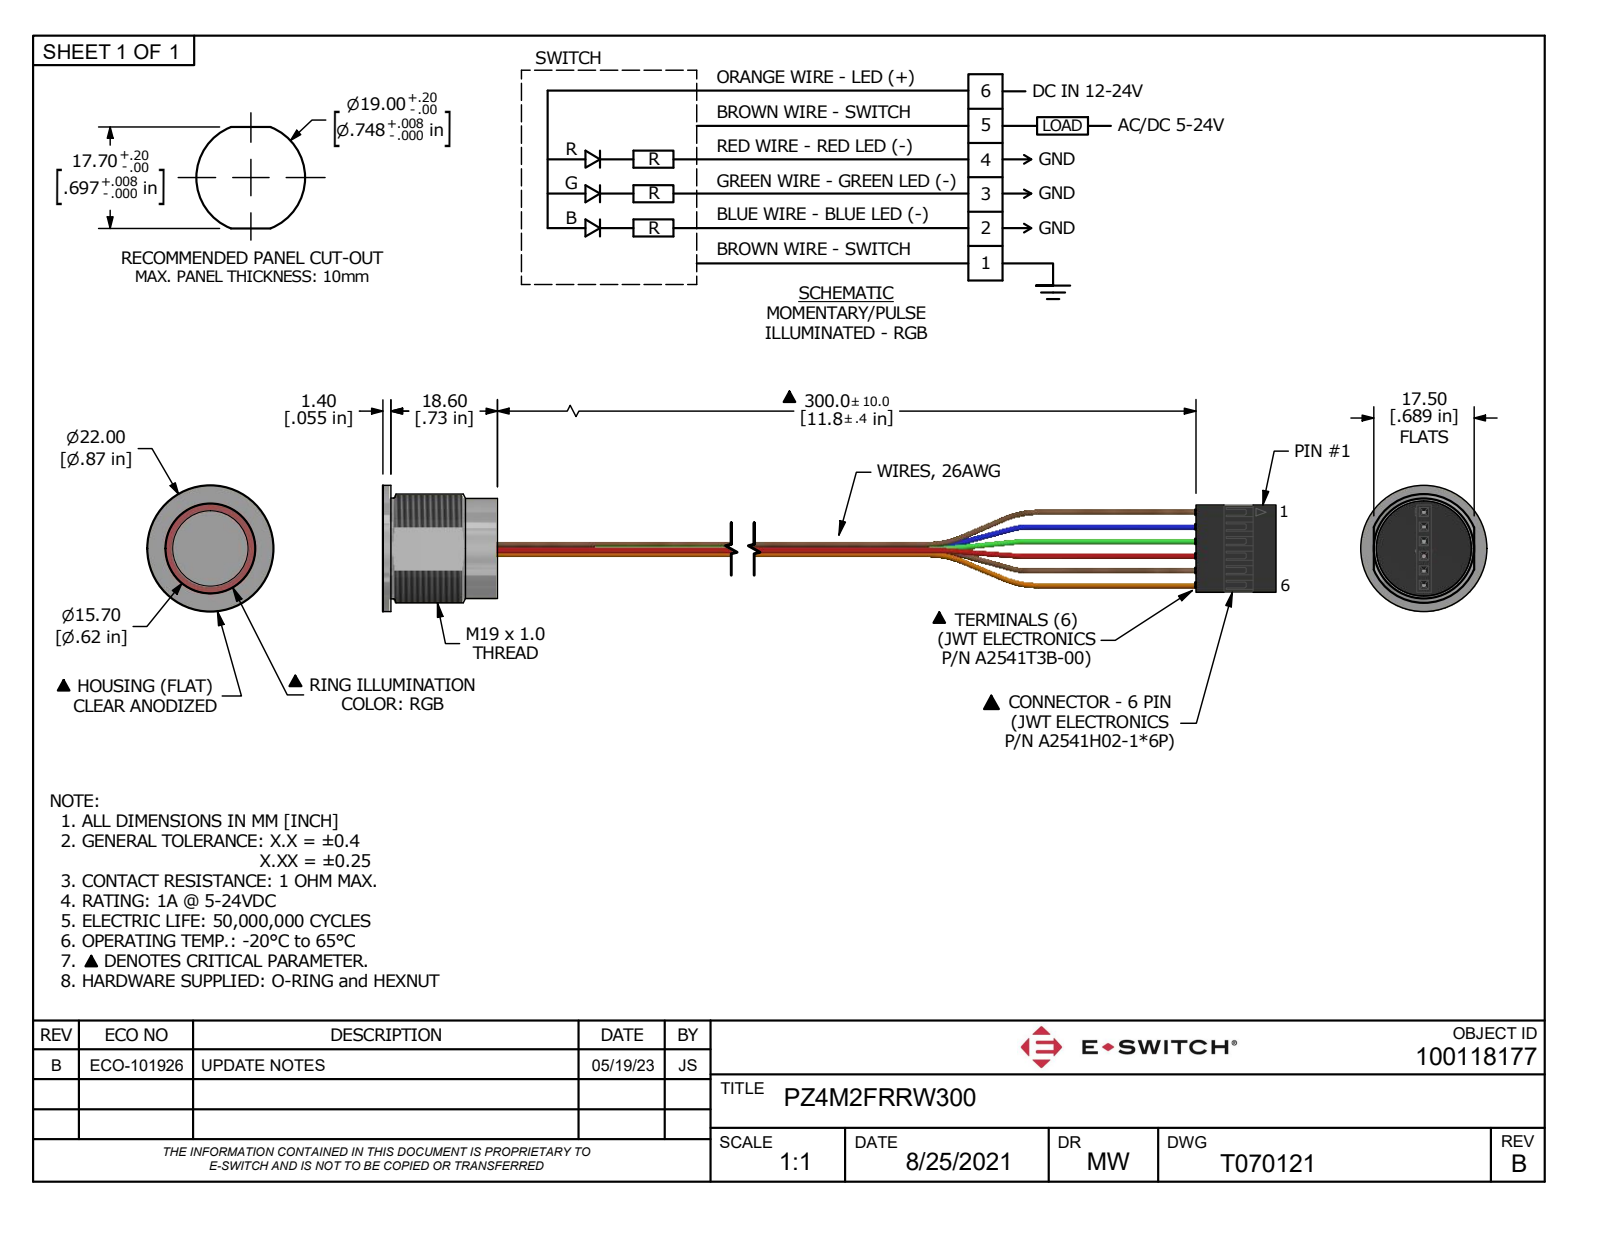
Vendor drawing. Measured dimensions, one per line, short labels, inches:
name: 100118177_Shrinkwrap_1
written by: Autodesk Inventor 2020 (AUTOMOTIVE_DESIGN)
unit: in
bodies: 5 solids, 210 faces (142 planar, 44 cylindrical, 24 other)
size: 13.15 × 0.866 × 0.866
volume: 0.439 in³; area: 13.47 in²
bosses: 16× ⌀0.039, 6× ⌀0.028, 1× ⌀0.866, 1× ⌀0.693, 1× ⌀0.689
rounds: 12× R0.01, 1× R0.374
face distances: 0.1, 0.081, 0.019, 0.294, 0.394, 0.063, 0.376, 0.313, 0.2, 0.055
